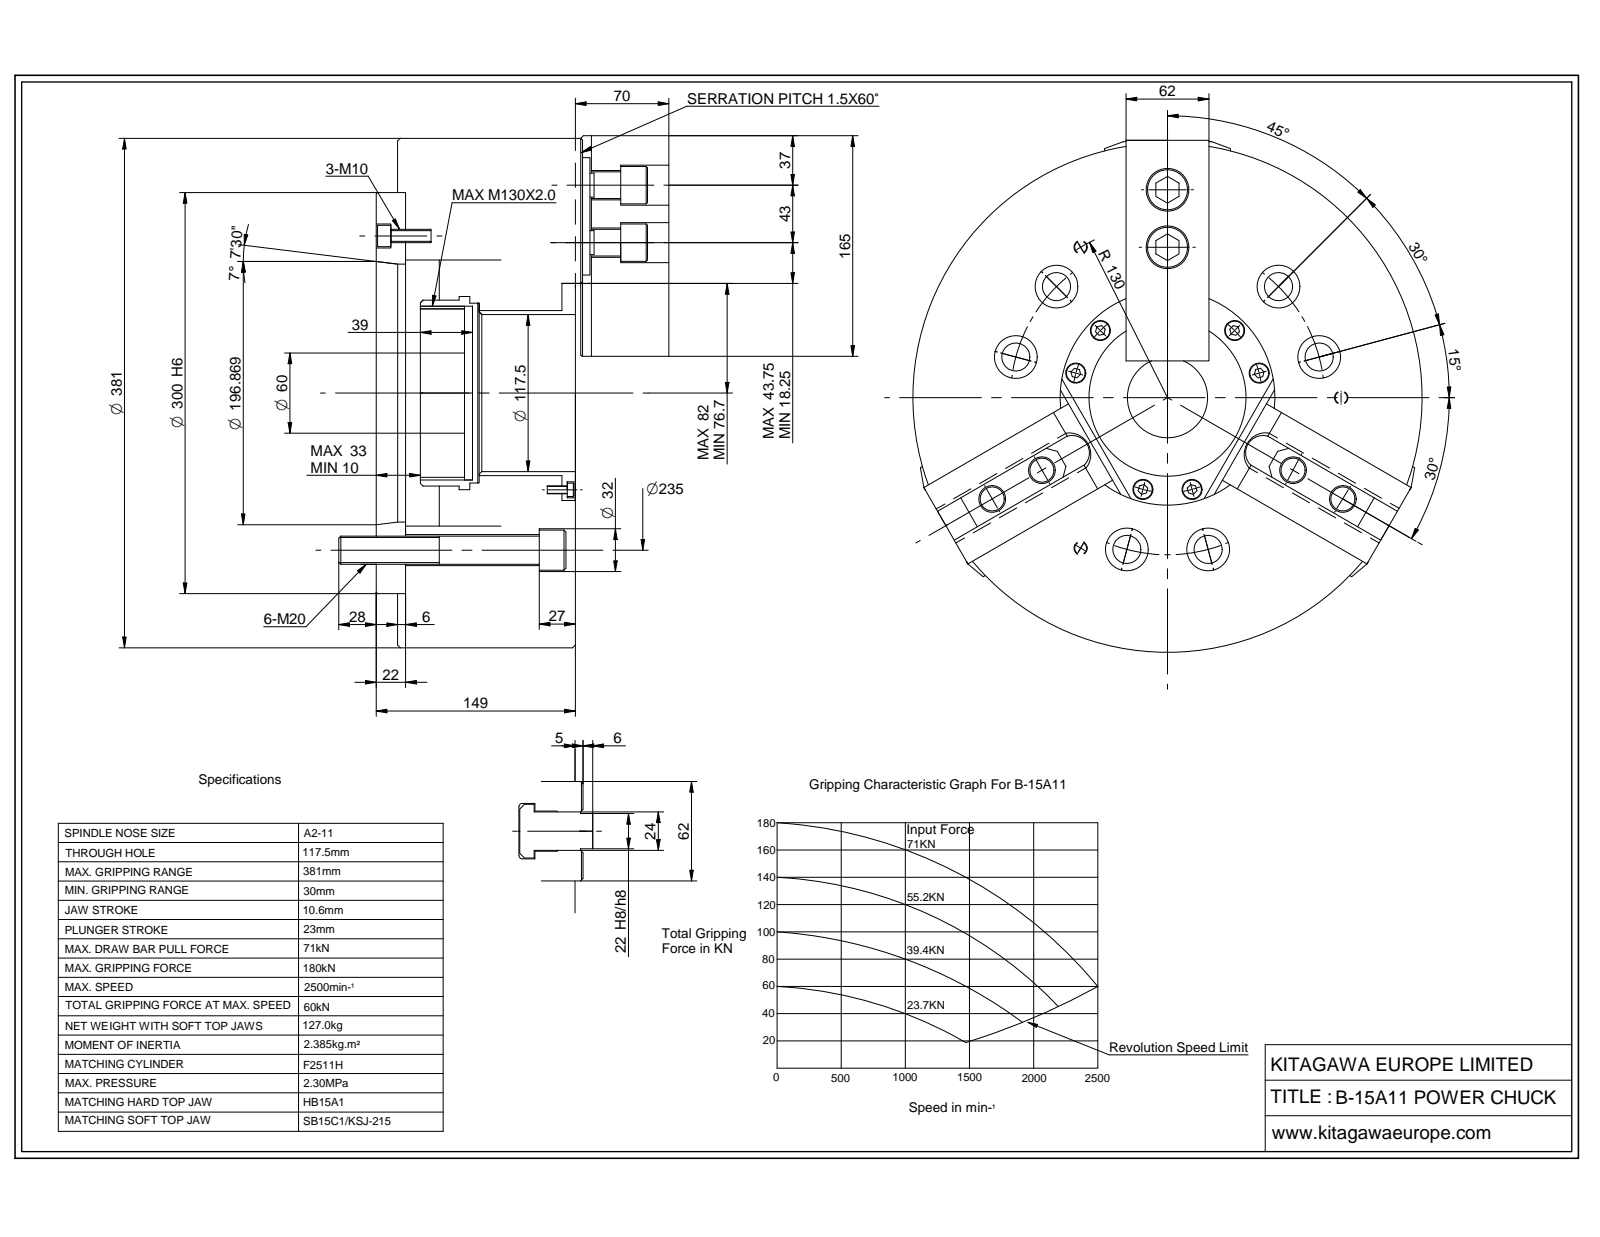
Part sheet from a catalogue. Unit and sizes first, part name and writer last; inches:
Units: inches
Overall size (bounding box): 11.811 × 11.811 × 0.866
Round holes (diameter × count): ⌀0.827 ×6, ⌀7.594 ×1
Round bosses / shafts (diameter × count): ⌀11.811 ×1
Main face-to-face distances: 0.866
Hole centre spacings: 4.626, 8.013, 8.937, 2.395, 4.626, 6.542, 8.013, 2.394
Volume: 52.29 in³ · Surface area: 186.8 in²
Bodies: 1 solid, 11 faces (2 planar, 8 cylindrical, 1 other)
Part name (STEP PRODUCT): B15A11; CB15A11
STEP written by: ST-DEVELOPER v16.7 (AUTOMOTIVE_DESIGN)
